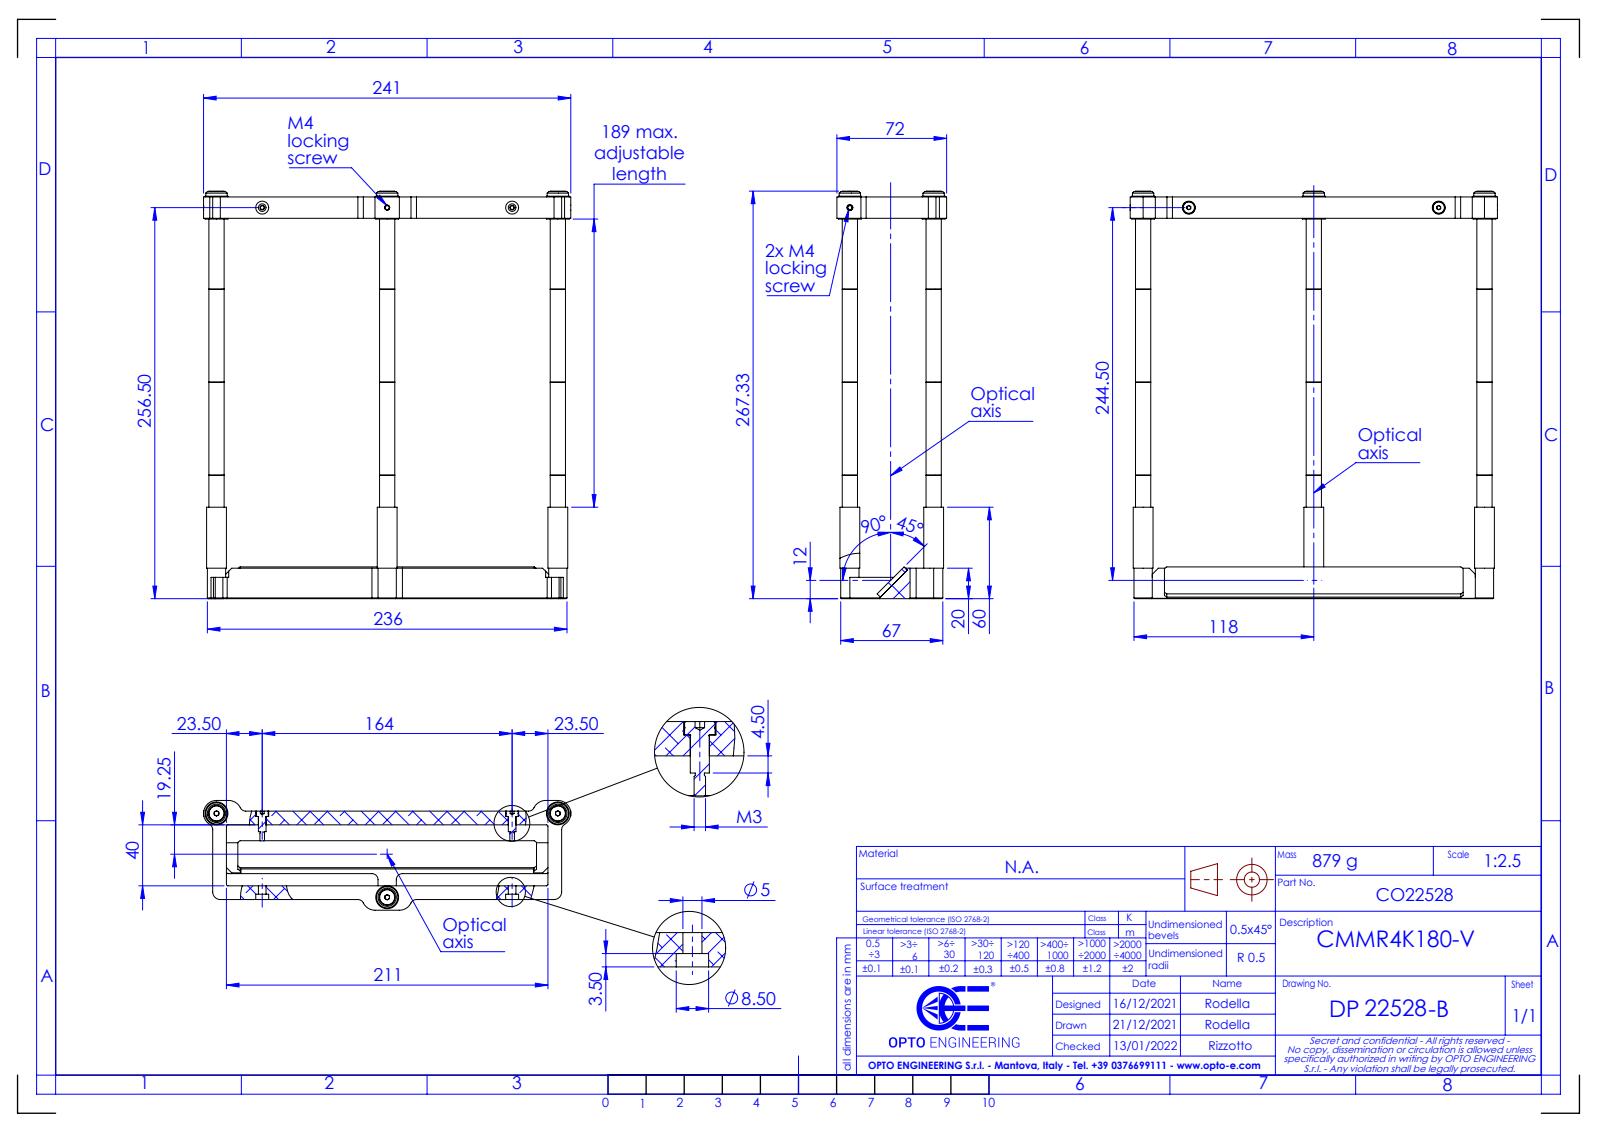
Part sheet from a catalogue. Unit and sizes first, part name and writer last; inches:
Units: inches
Overall size (bounding box): 10.524 × 9.488 × 2.835
Round holes (diameter × count): ⌀0.197 ×2, ⌀0.335 ×2
Round bosses / shafts (diameter × count): ⌀0.591 ×3, ⌀0.551 ×3, ⌀0.512 ×3, ⌀0.394 ×3, ⌀0.388 ×3, ⌀0.472 ×2, ⌀0.315 ×2, ⌀0.118 ×2
Partial cylindrical surfaces — rounded edges, fillets, slot ends (radius × count): R0.157 ×14, R0.335 ×6, R0.039 ×4, R0.079 ×2, R0.197 ×2, R0.236 ×1
Main face-to-face distances: 0.354, 0.551, 9.823, 10.374, 0.118, 1.929, 0.315, 1.575, 1.26, 1.614
Hole centre spacings: 6.457
Bodies: 0 solids, 281 faces (132 planar, 115 cylindrical, 34 other)
Part name (STEP PRODUCT): DP22528-B_CMMR4K180-V
STEP written by: SolidWorks 2021 (CONFIG_CONTROL_DESIGN)
